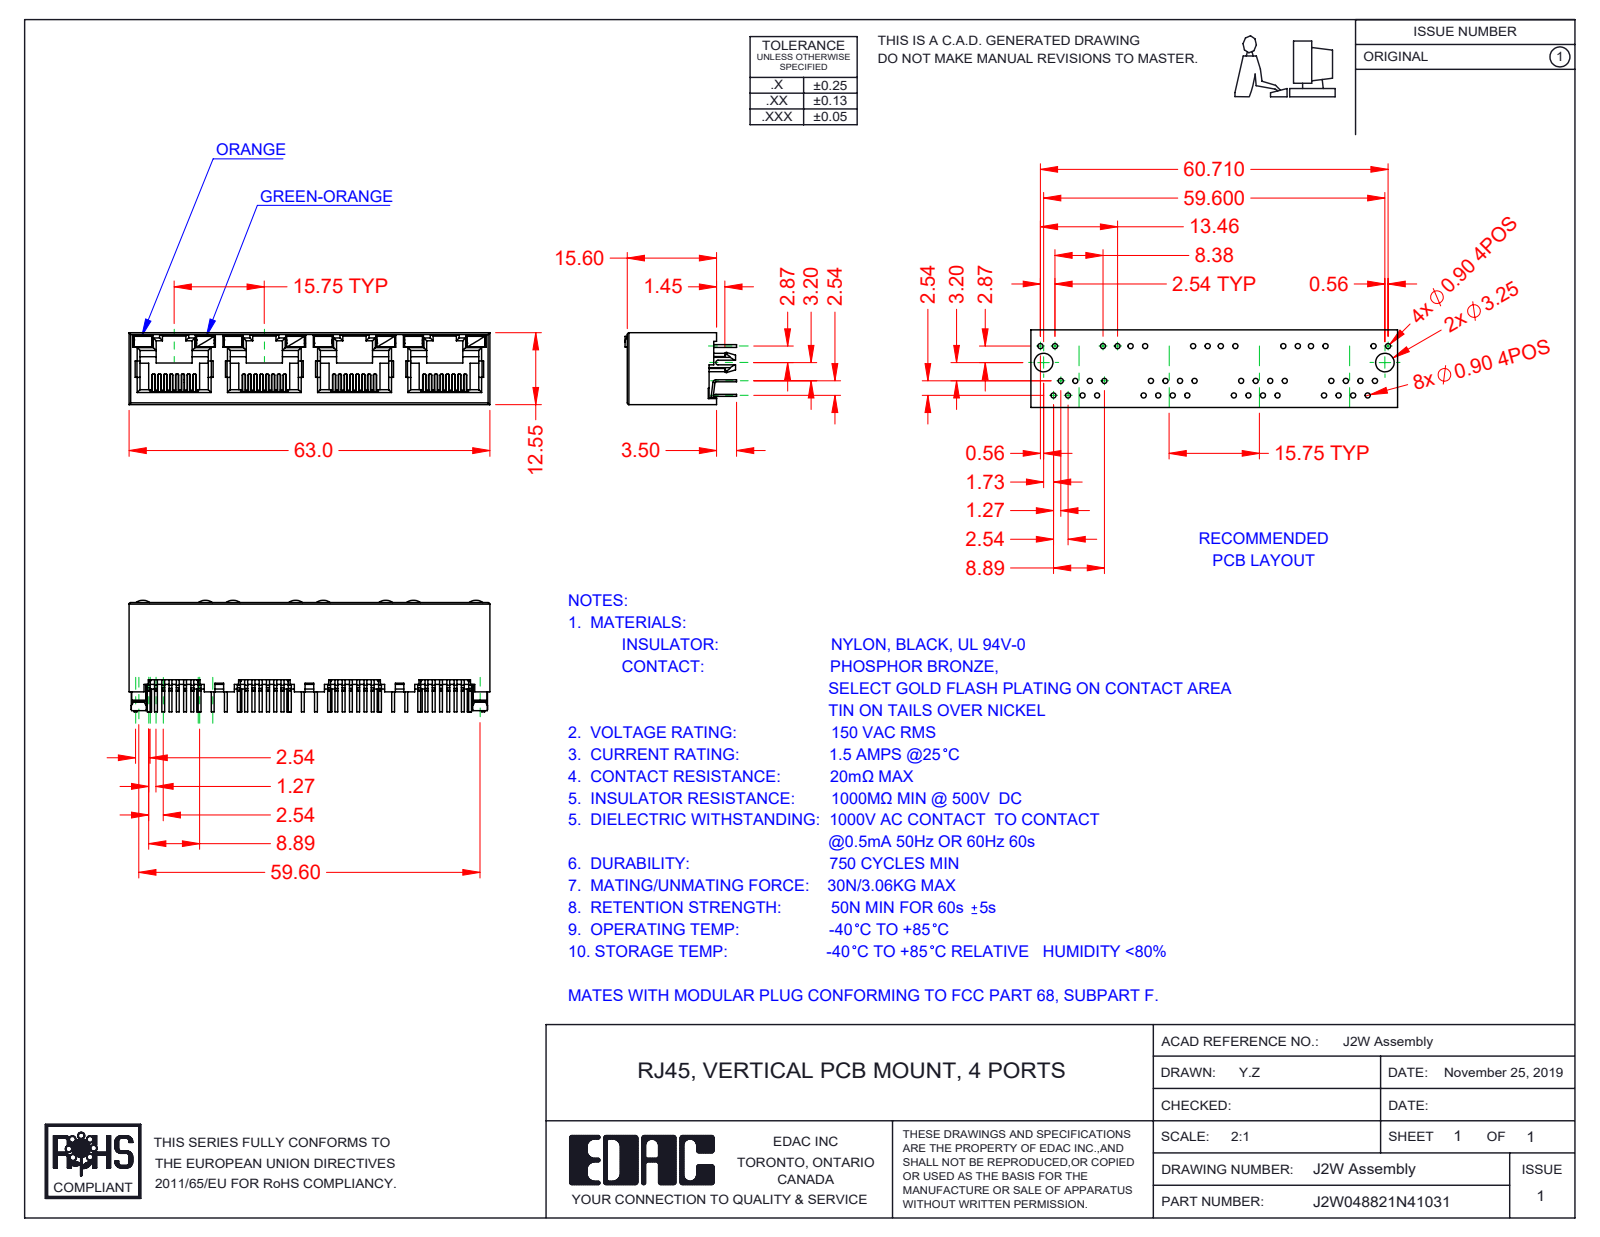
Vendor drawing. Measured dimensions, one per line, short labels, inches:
name: 2W Contacts; 2W LED LH_4-Orange; 2W Insulator; 2W Contact Lock (+2 more)
written by: SolidWorks 2016 (CONFIG_CONTROL_DESIGN)
unit: in
bodies: 45 solids, 3139 faces (2600 planar, 481 cylindrical, 58 other)
size: 2.48 × 0.768 × 0.494
volume: 0.326 in³; area: 20.37 in²
rounds: 64× R0.006, 29× R0.008, 28× R0.02, 14× R0.012, 8× R0.018, 8× R0.079, 2× R0.01, 2× R0.059
face distances: 0.494, 0.469, 0.026, 0.62, 0.014, 0.059, 0.031, 0.024, 0.445, 1.24
